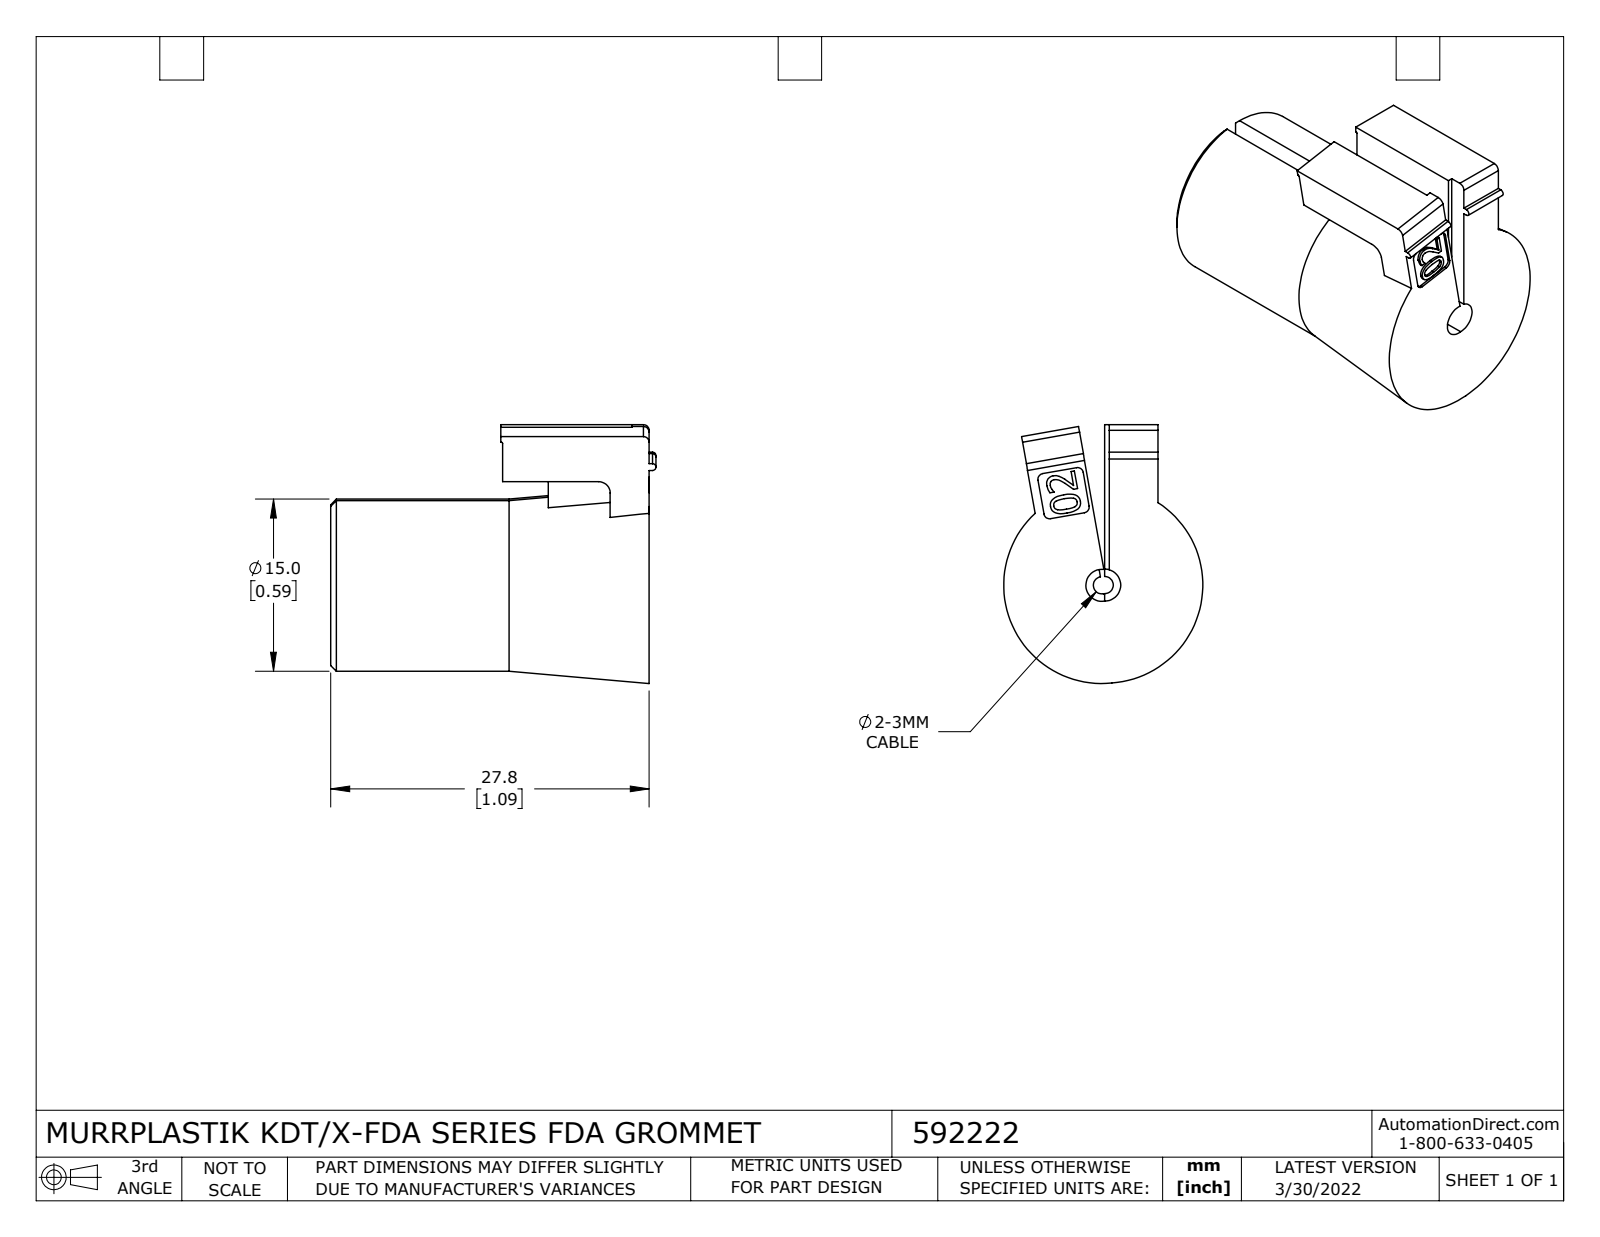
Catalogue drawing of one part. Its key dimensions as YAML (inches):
part_name: "592222"
step_written_by: "SolidWorks 2021 (CONFIG_CONTROL_DESIGN)"
units: inches
bodies: {solids: 1, faces: 119, planar: 58, cylindrical: 25, other: 36}
overall_size: [1.118, 0.889, 0.684]
volume: 0.34
surface_area: 4.393
partial_cylinders:
  - {radius: 0.02, count: 6}
  - {radius: 0.004, count: 2}
  - {radius: 0.012, count: 2}
  - {radius: 0.03, count: 2}
  - {radius: 0.039, count: 2}
  - {radius: 0.055, count: 2}
  - {radius: 0.295, count: 2}
face_to_face_distances: [1.094, 0.183, 0.157, 0.016, 0.504, 0.591, 0.167, 0.199, 0.346, 0.748]
